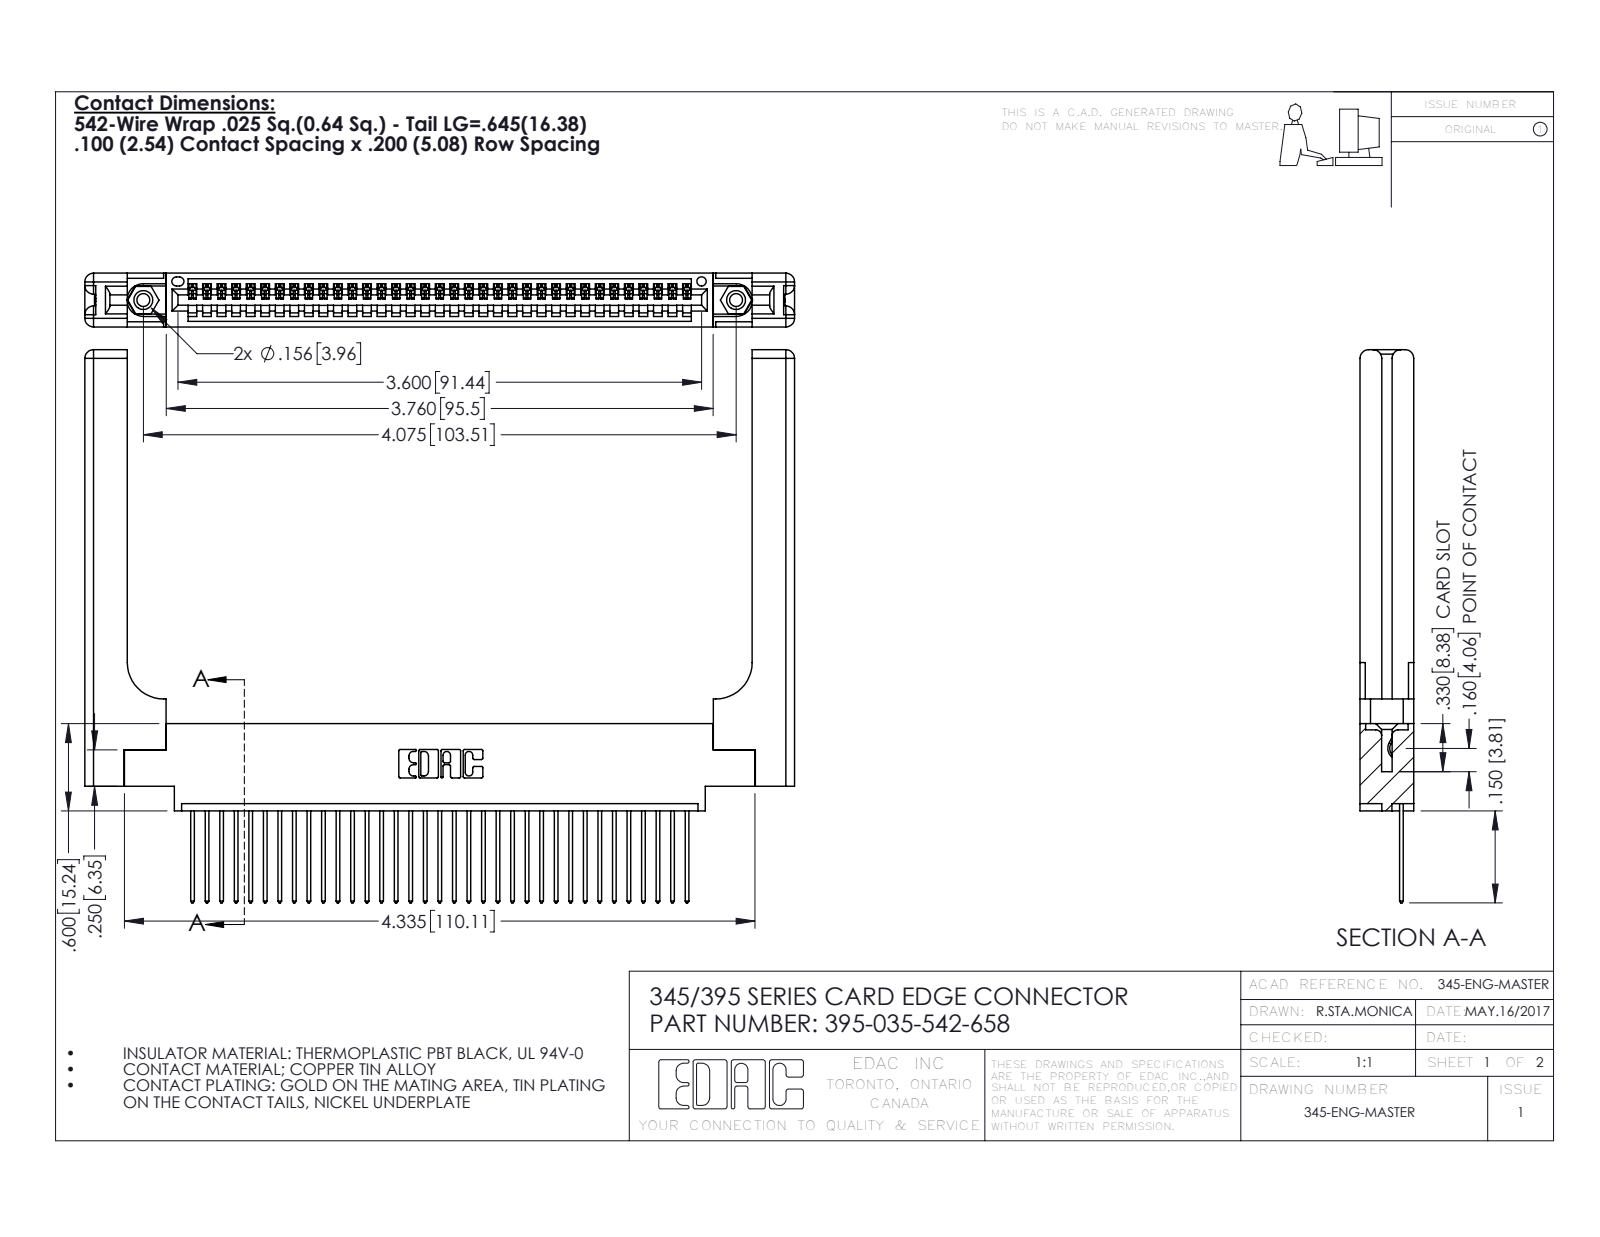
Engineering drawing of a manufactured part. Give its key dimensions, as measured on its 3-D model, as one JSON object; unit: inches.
{"part_name": "345-250-001_345-250-001-102; 345-220-058_345-220-058; 345-292-001_345-293-142; 395-035-542-658 (+1 more)", "step_written_by": "SolidWorks 2016 (CONFIG_CONTROL_DESIGN)", "units": "inches", "bodies": {"solids": 40, "faces": 2416, "planar": 1632, "cylindrical": 724, "other": 60}, "overall_size": [4.879, 3.802, 0.37], "volume_in3": 1.232, "surface_area_in2": 33.09, "round_holes": [[0.089, 2], [0.125, 2], [0.156, 2], [0.064, 1]], "round_bosses_or_shafts": [[0.155, 2]], "partial_cylinders_radius": [[0.006, 70], [0.01, 70], [0.01, 22], [0.06, 16], [0.007, 6], [0.031, 6], [0.026, 3], [0.03, 2]], "face_to_face_distances": [0.37, 0.072, 0.298, 0.098, 0.272, 0.025, 0.2, 0.148, 0.15, 0.225], "hole_center_spacings": [0.27, 3.839, 4.075]}
